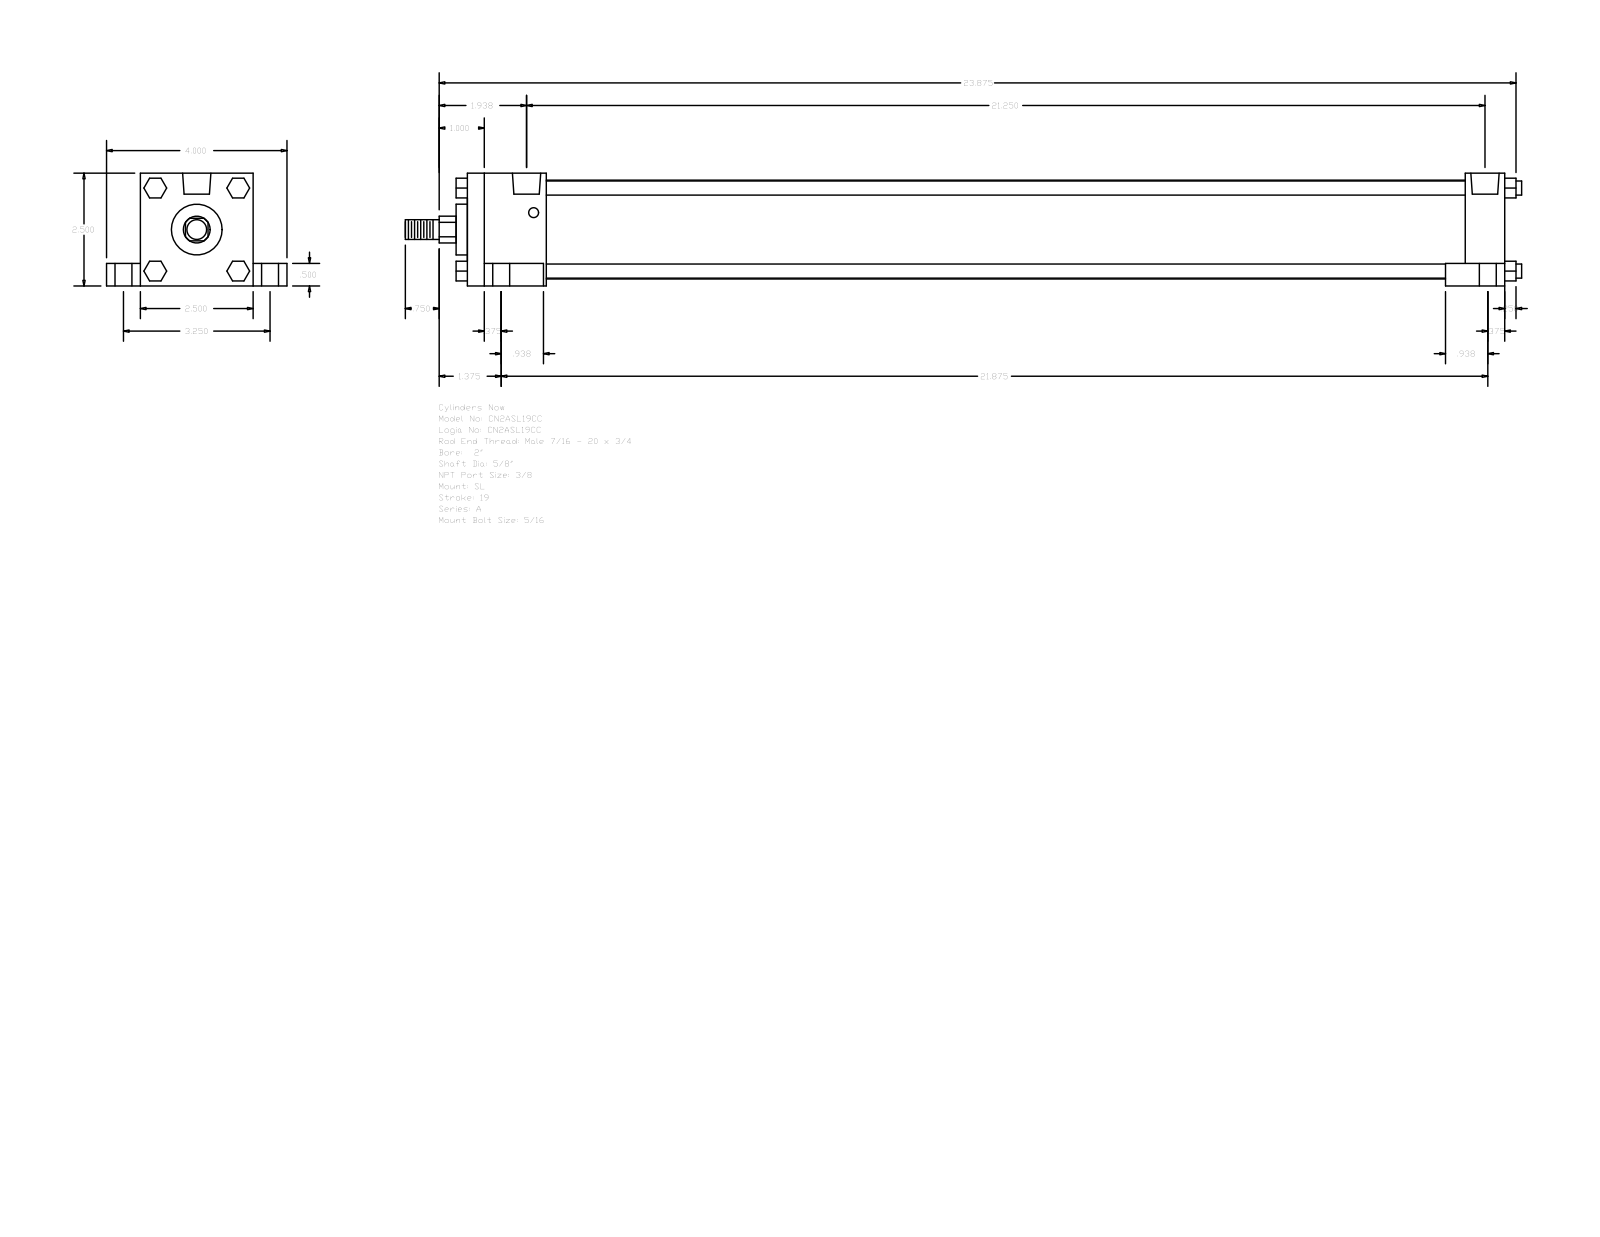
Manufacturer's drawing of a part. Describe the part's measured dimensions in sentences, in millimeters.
The part is named "A_SL__0200_0.625". Its 3-D file was written by "GSSL Pune (CONFIG_CONTROL_DESIGN)". It is 0 solids with 148 faces: 112 planar, 36 cylindrical and 0 other. Overall it measures 628.65 by 101.6 by 63.5 millimeters. Round holes: 4 of diameter 5.56, 4 of diameter 9.53, 4 of diameter 15.88, 2 of diameter 15.93. Round bosses or shafts: 4 of diameter 7.94, 1 of diameter 55.63, 1 of diameter 28.57, 1 of diameter 15.88, 1 of diameter 11.11. Partial cylindrical surfaces (rounded edges, fillets, slot ends): 1 of radius 7.54. The main face-to-face distances are 63.5, 584.2, 50.8, 12.7, 19.05, 82.55, 44.45, 539.75, 561.97, 517.52. The hole center spacings are 41.3, 41.64, 43.67, 45.13, 82.54, 531.8, 538.94, 542.91.
